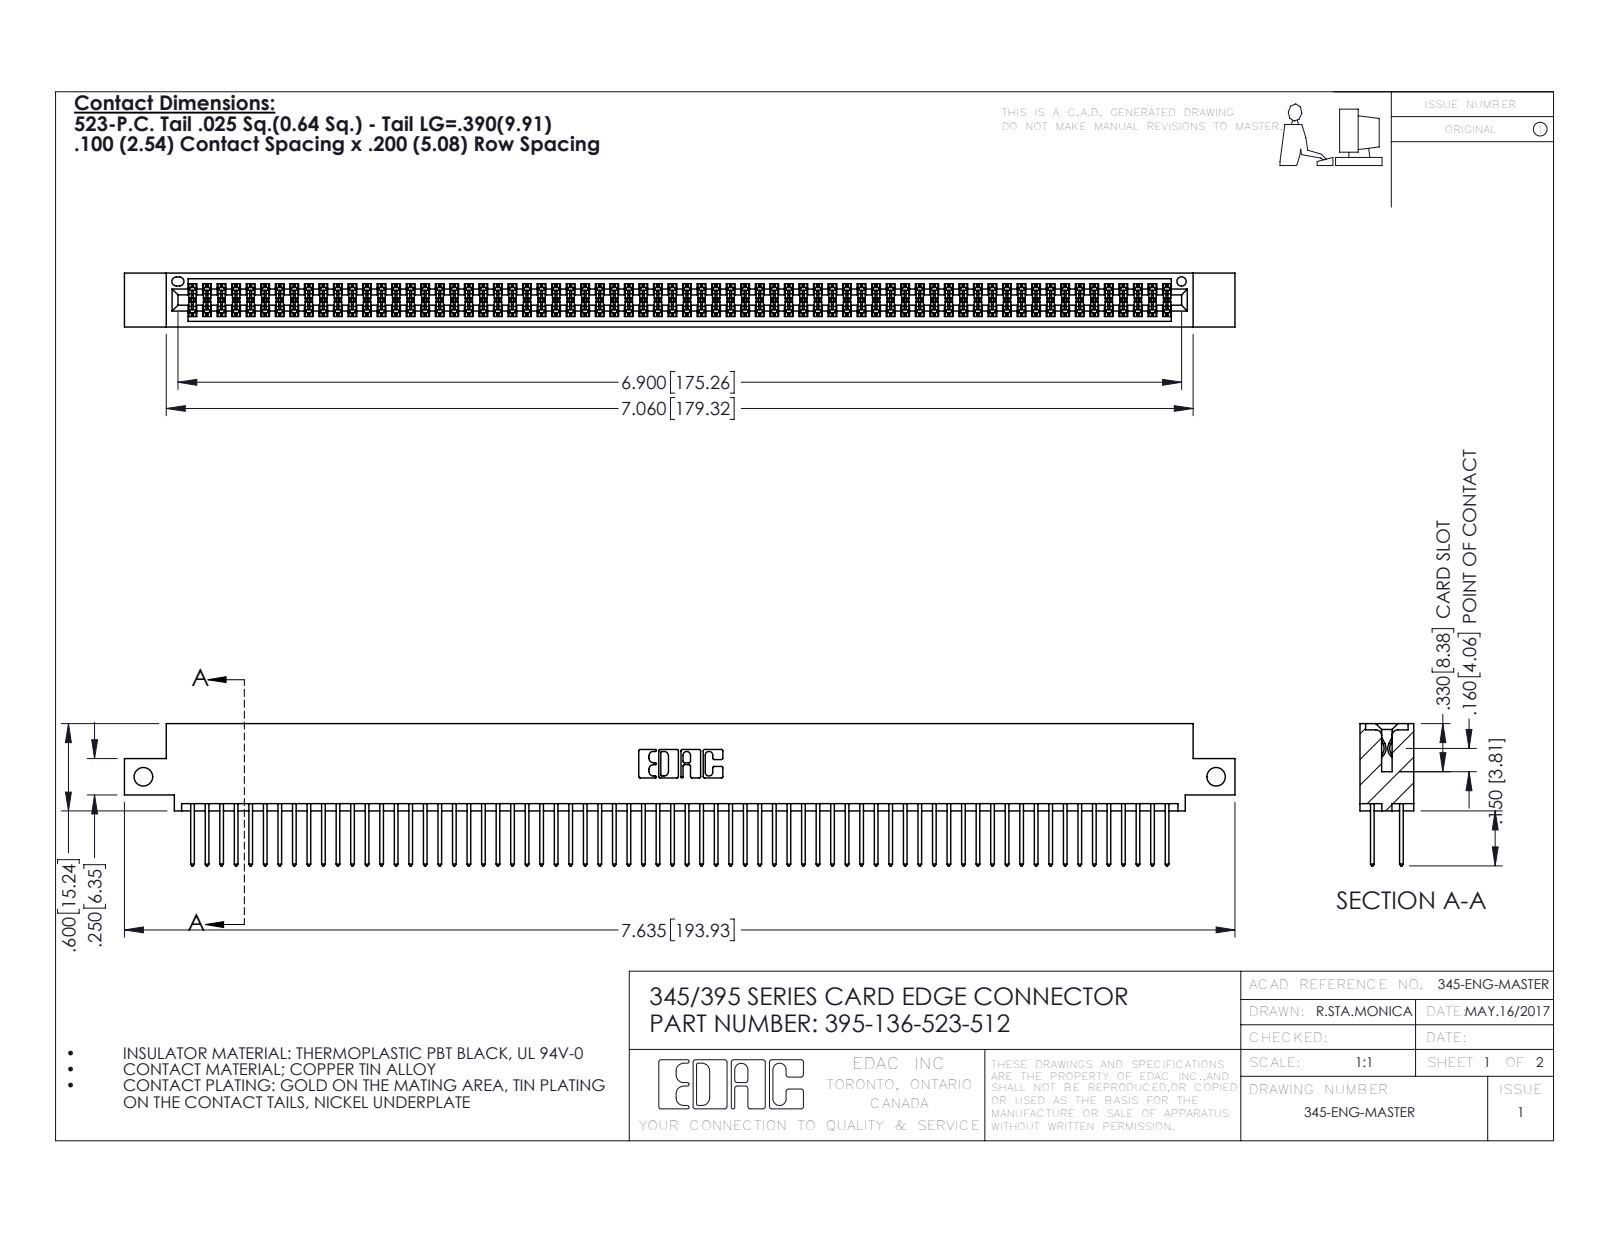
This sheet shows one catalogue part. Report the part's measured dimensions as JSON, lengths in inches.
{"part_name": "395-136-523-512; 345-292-001_345-293-123; 345 Part_0.110 Offset - Side Mount", "step_written_by": "SolidWorks 2016 (CONFIG_CONTROL_DESIGN)", "units": "inches", "bodies": {"solids": 137, "faces": 6930, "planar": 4572, "cylindrical": 2358, "other": 0}, "overall_size": [7.635, 0.977, 0.37], "volume_in3": 1.172, "surface_area_in2": 46.64, "round_holes": [[0.128, 2], [0.064, 1]], "partial_cylinders_radius": [[0.006, 204], [0.01, 136], [0.01, 22], [0.007, 6], [0.031, 6], [0.026, 3], [0.014, 2], [0.019, 2]], "face_to_face_distances": [0.072, 0.298, 0.2, 0.098, 0.272, 0.025, 0.37, 0.225, 0.175, 0.149], "hole_center_spacings": [7.375]}
